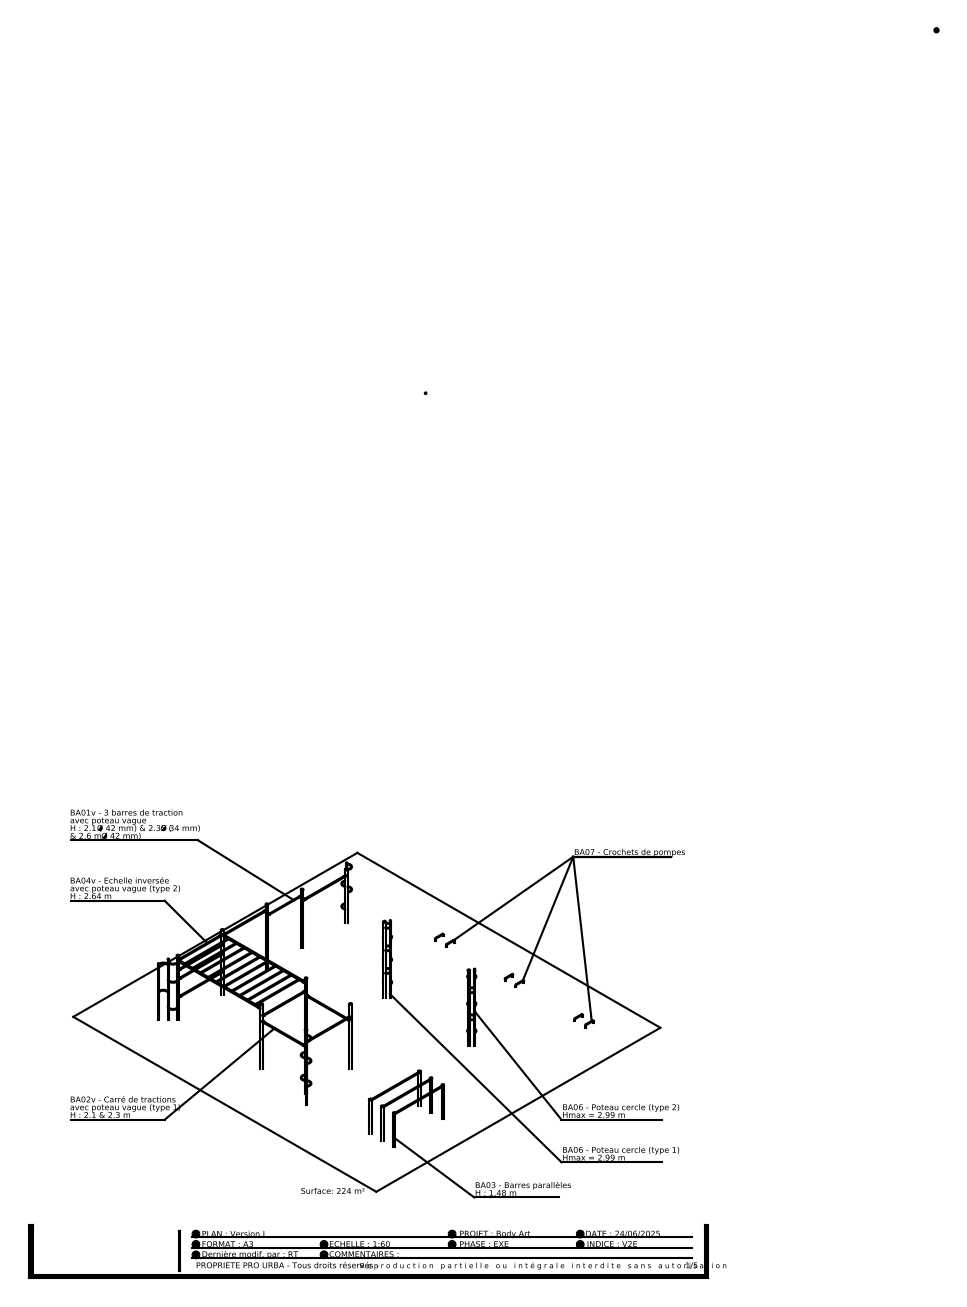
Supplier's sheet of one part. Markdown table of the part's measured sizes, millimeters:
| quantity | value |
| --- | --- |
| part name | Traverse + visserie_Diam. 42.4; Poteau_Poteau double 90° - 2100 & 2300 + vague; Poteau_Poteau double 180° - 2100 & 2350 avec diam33.7 sur h2300; Barres parallèles_BP entraxe 2390 V2 (+8 more) |
| STEP written by | SolidWorks 2025 (AUTOMOTIVE_DESIGN) |
| units | millimeters |
| bodies | 264 solids, 4742 faces (1474 planar, 1636 cylindrical, 1632 other) |
| overall size | 15454 × 14489 × 3875 |
| round holes (diameter × count) | 6.65 × 40, 8 × 40, 8.75 × 40, 9 × 40, 15 × 40, 43.4 × 23, 36 × 22, 29.7 × 18, 84.9 × 17, 37.2 × 13, 20 × 12, 38.4 × 12 |
| round bosses / shafts (diameter × count) | 13 × 40, 42.4 × 35, 33.7 × 19, 88.9 × 17, 35 × 10, 60.3 × 2, 52.1 × 2, 27 × 1 |
| main face-to-face distances | 60, 150, 2100.2, 200, 95, 2640.2, 500, 35, 2300.2, 540 |
| hole center spacings | 2270, 130.08, 38, 71, 109, 400, 4270, 800 |
